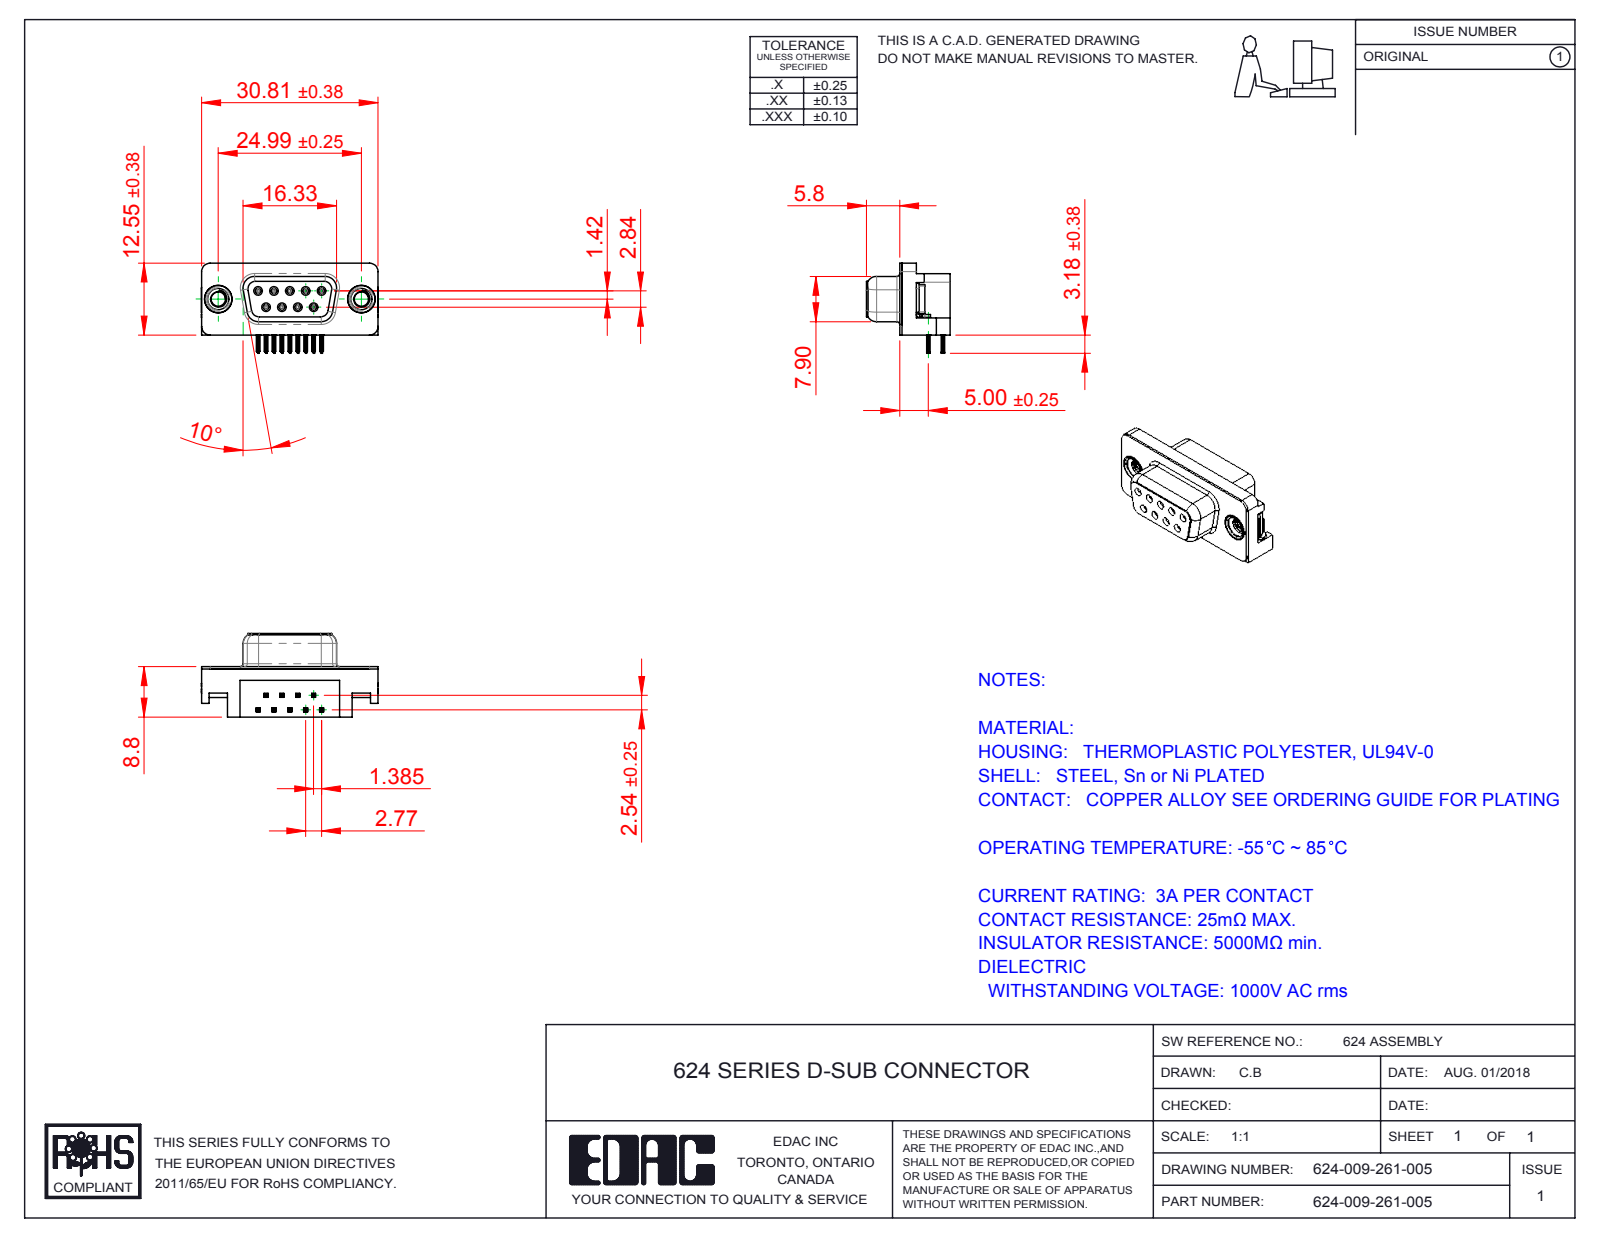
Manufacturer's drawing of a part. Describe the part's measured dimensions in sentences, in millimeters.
The part is named "624 Non Board Mount; 624 Contact Top; 624 Socket Bottom; 624 Shell_9 Socket (+3 more)". Its 3-D file was written by "SolidWorks 2016 (CONFIG_CONTROL_DESIGN)". It is 15 solids with 1520 faces: 642 planar, 410 cylindrical and 468 other. Overall it measures 30.89 by 15.73 by 14.6 millimeters. Its volume is 2 932 cubic millimeters and its surface area 4 338 square millimeters. Round holes: 9 of diameter 0.8, 9 of diameter 0.9, 2 of diameter 2.5, 2 of diameter 4, 2 of diameter 4.8, 2 of diameter 5. Round bosses or shafts: 9 of diameter 1.2, 2 of diameter 4.9, 2 of diameter 4.75, 2 of diameter 3.9. Partial cylindrical surfaces (rounded edges, fillets, slot ends): 72 of radius 0.1, 36 of radius 0.15, 18 of radius 0.35, 18 of radius 1, 9 of radius 0.34, 8 of radius 0.25, 8 of radius 1.35, 7 of radius 1.5. The main face-to-face distances are 0.4, 8.4, 8.8, 2.9, 2.5, 6.2, 5.9, 0.35, 10.69, 10.34. The hole center spacings are 3.16, 2.77, 5.54, 5.03, 5.04, 8.31, 7.48, 7.49.
